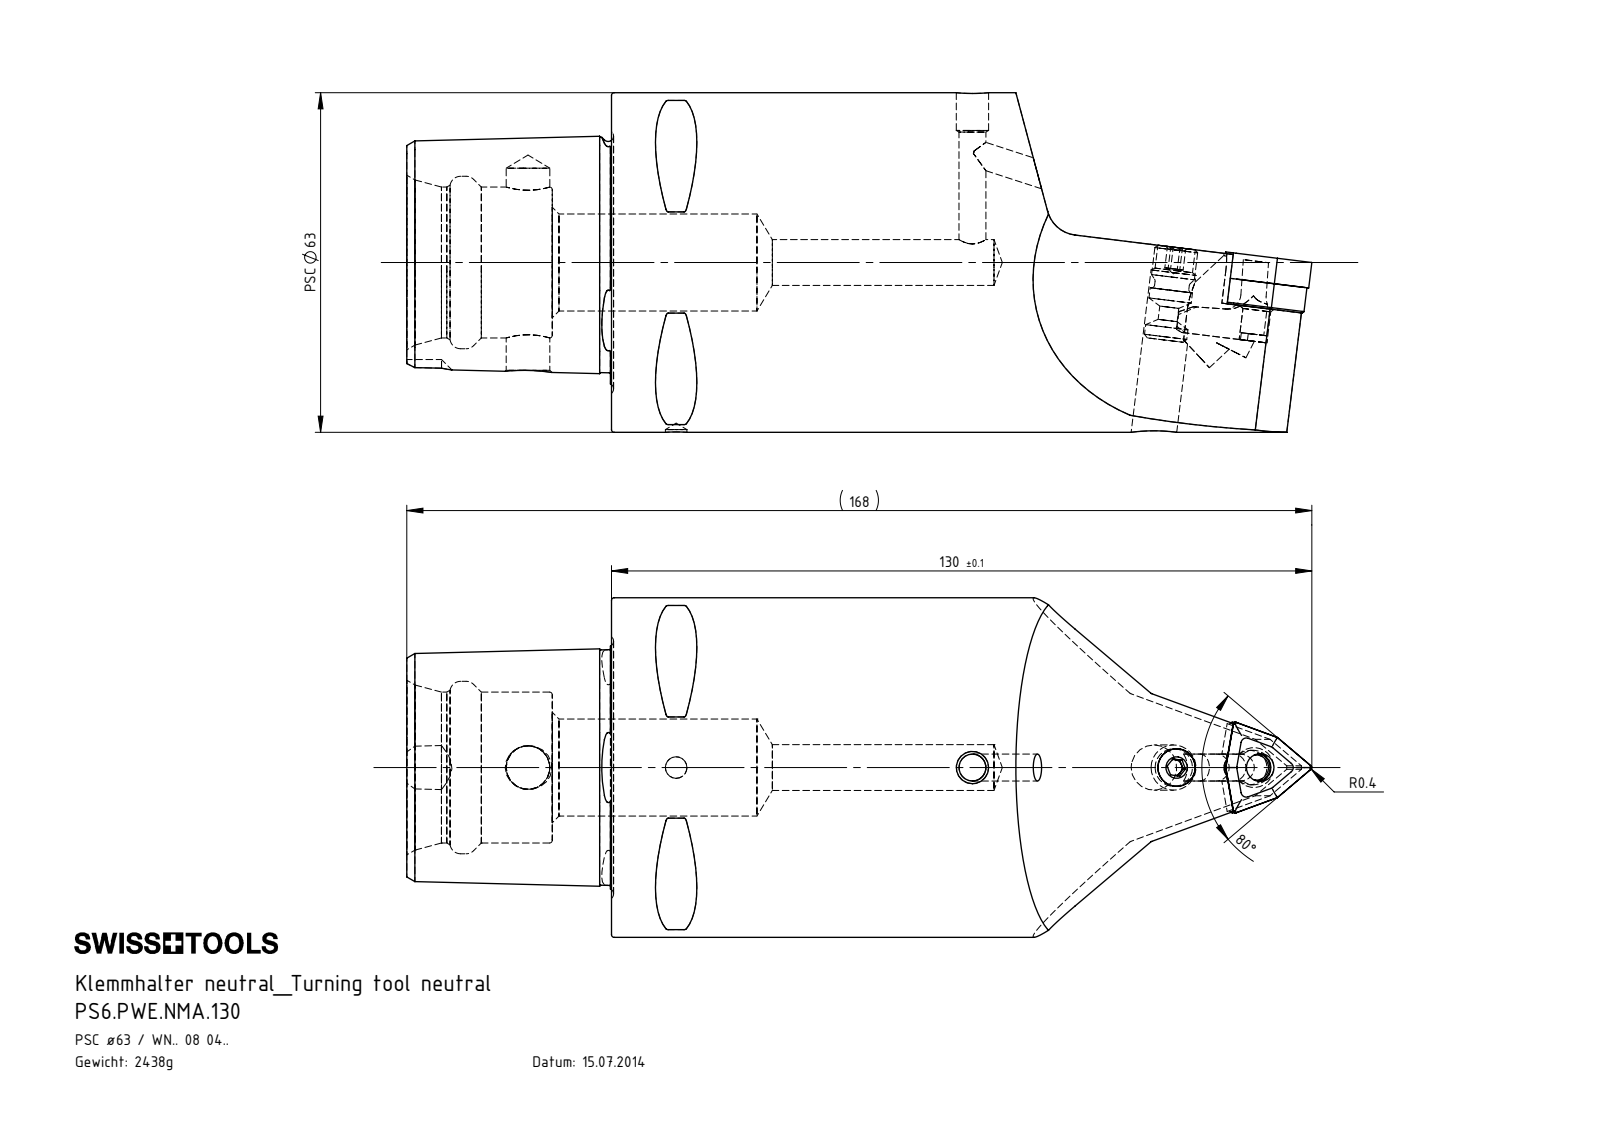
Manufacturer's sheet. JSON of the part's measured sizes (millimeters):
{"part_name": "PS6-PWE.NMA.130; WCD-ER4.101.017_A; WCD-ER1.101.000; KVT_MB_600_060 (+4 more)", "step_written_by": "SolidWorks 2017 (CONFIG_CONTROL_DESIGN)", "units": "millimeters", "bodies": {"solids": 8, "faces": 351, "planar": 101, "cylindrical": 84, "other": 166}, "overall_size": [168, 63, 63], "volume_mm3": 310016, "surface_area_mm2": 41269, "round_holes": [[5, 3], [4, 1], [5.16, 1], [6, 1], [6.7, 1], [7, 1], [7.8, 1], [8.1, 1], [8.4, 1], [8.5, 1], [18, 1], [28, 1]], "round_bosses_or_shafts": [[63, 1], [8, 1], [7.9, 1], [6.4, 1], [6, 1], [4.7, 1], [3.55, 1]], "partial_cylinders_radius": [[0.5, 8], [0.4, 3], [1, 3], [2.5, 3], [0.8, 2], [6, 2], [2.3, 1], [2.35, 1]], "face_to_face_distances": [38, 8.51, 24.88, 4.46, 27, 11, 4.77, 9.23, 55.8, 4.85], "hole_center_spacings": [15.6, 27.5, 55, 82.5]}
